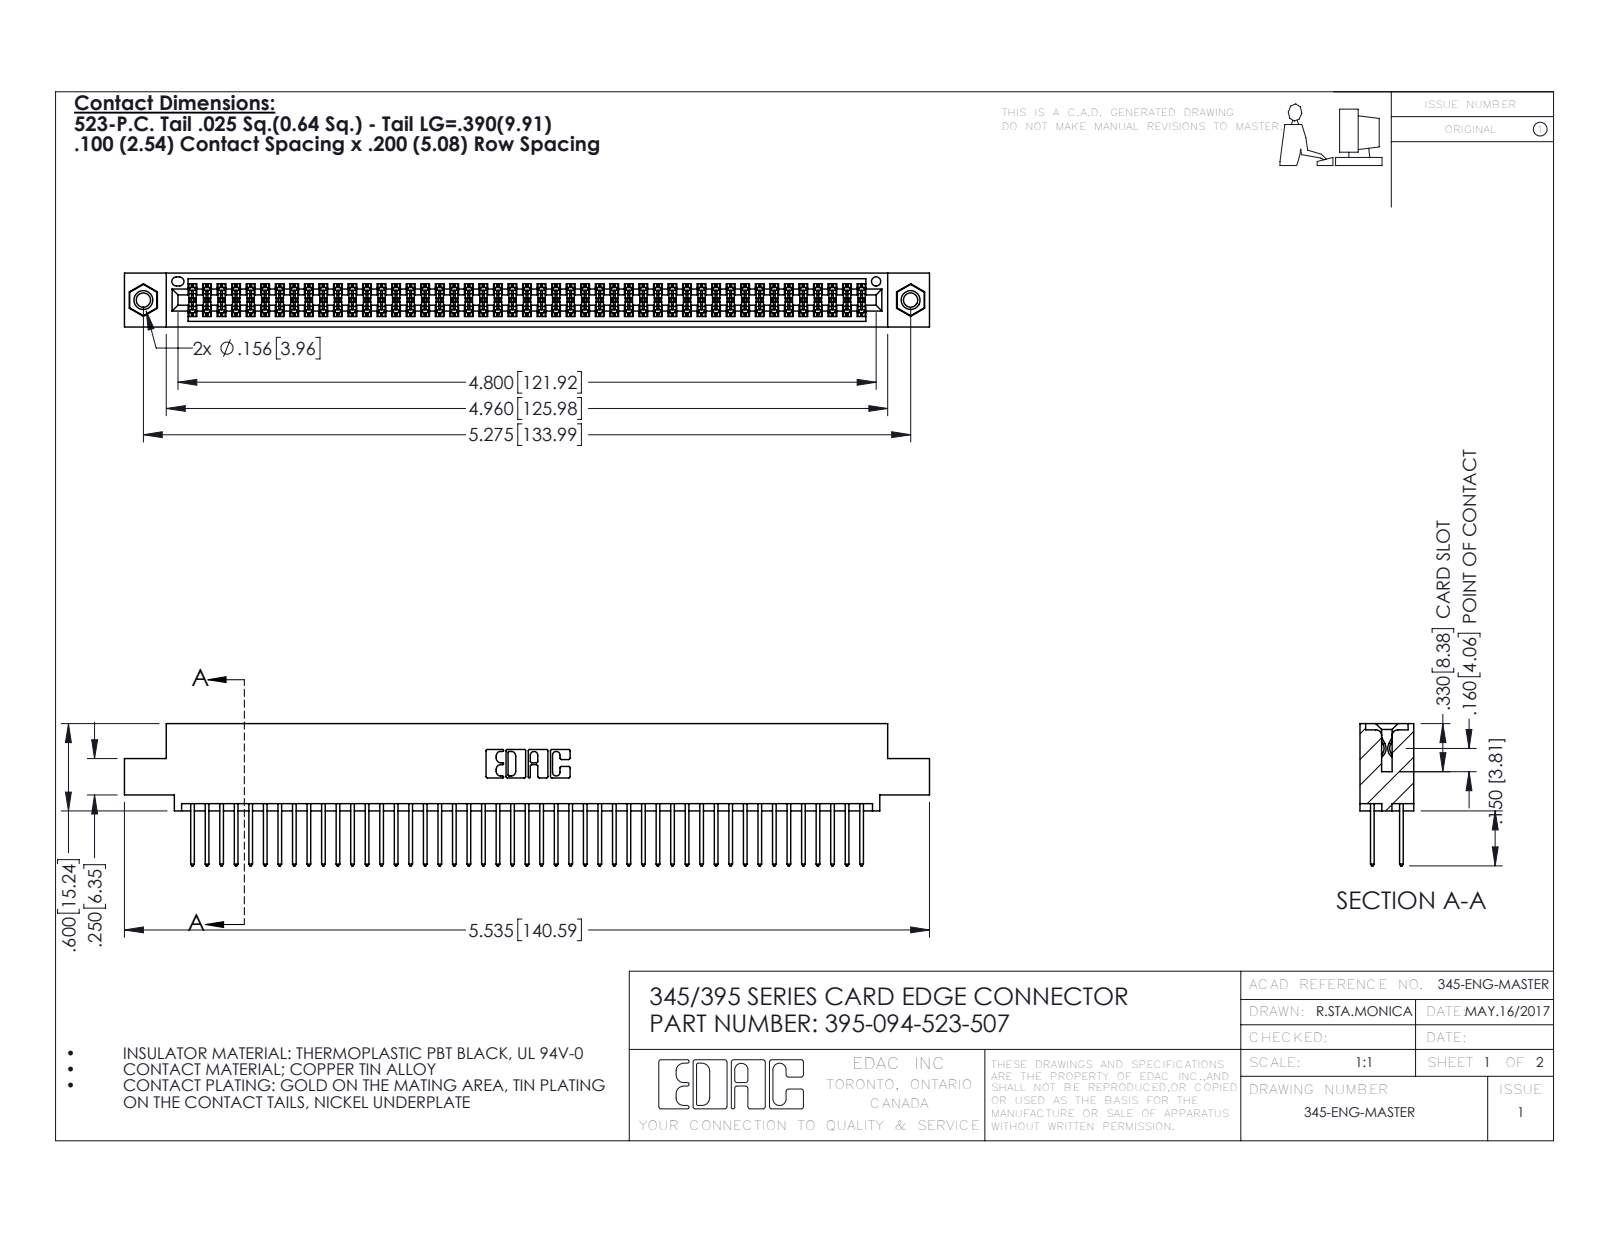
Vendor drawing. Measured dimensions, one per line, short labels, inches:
name: 345-250-001_345-250-005-103; 345-292-001_345-293-123; 345 Part_0.110 Offset - 0.156 Dia-TI; 395-094-523-507
written by: SolidWorks 2016 (CONFIG_CONTROL_DESIGN)
unit: in
bodies: 97 solids, 4890 faces (3218 planar, 1656 cylindrical, 16 other)
size: 5.535 × 0.977 × 0.37
volume: 0.843 in³; area: 33.32 in²
holes: 2× ⌀0.098, 2× ⌀0.125, 2× ⌀0.156, 1× ⌀0.064
bosses: 2× ⌀0.155
rounds: 141× R0.006, 94× R0.01, 22× R0.01, 6× R0.007, 6× R0.031, 3× R0.026, 2× R0.014, 2× R0.019
face distances: 0.072, 0.298, 0.2, 0.098, 0.272, 0.025, 0.37, 0.225, 0.175, 0.149
hole spacings: 0.27, 5.039, 5.275
